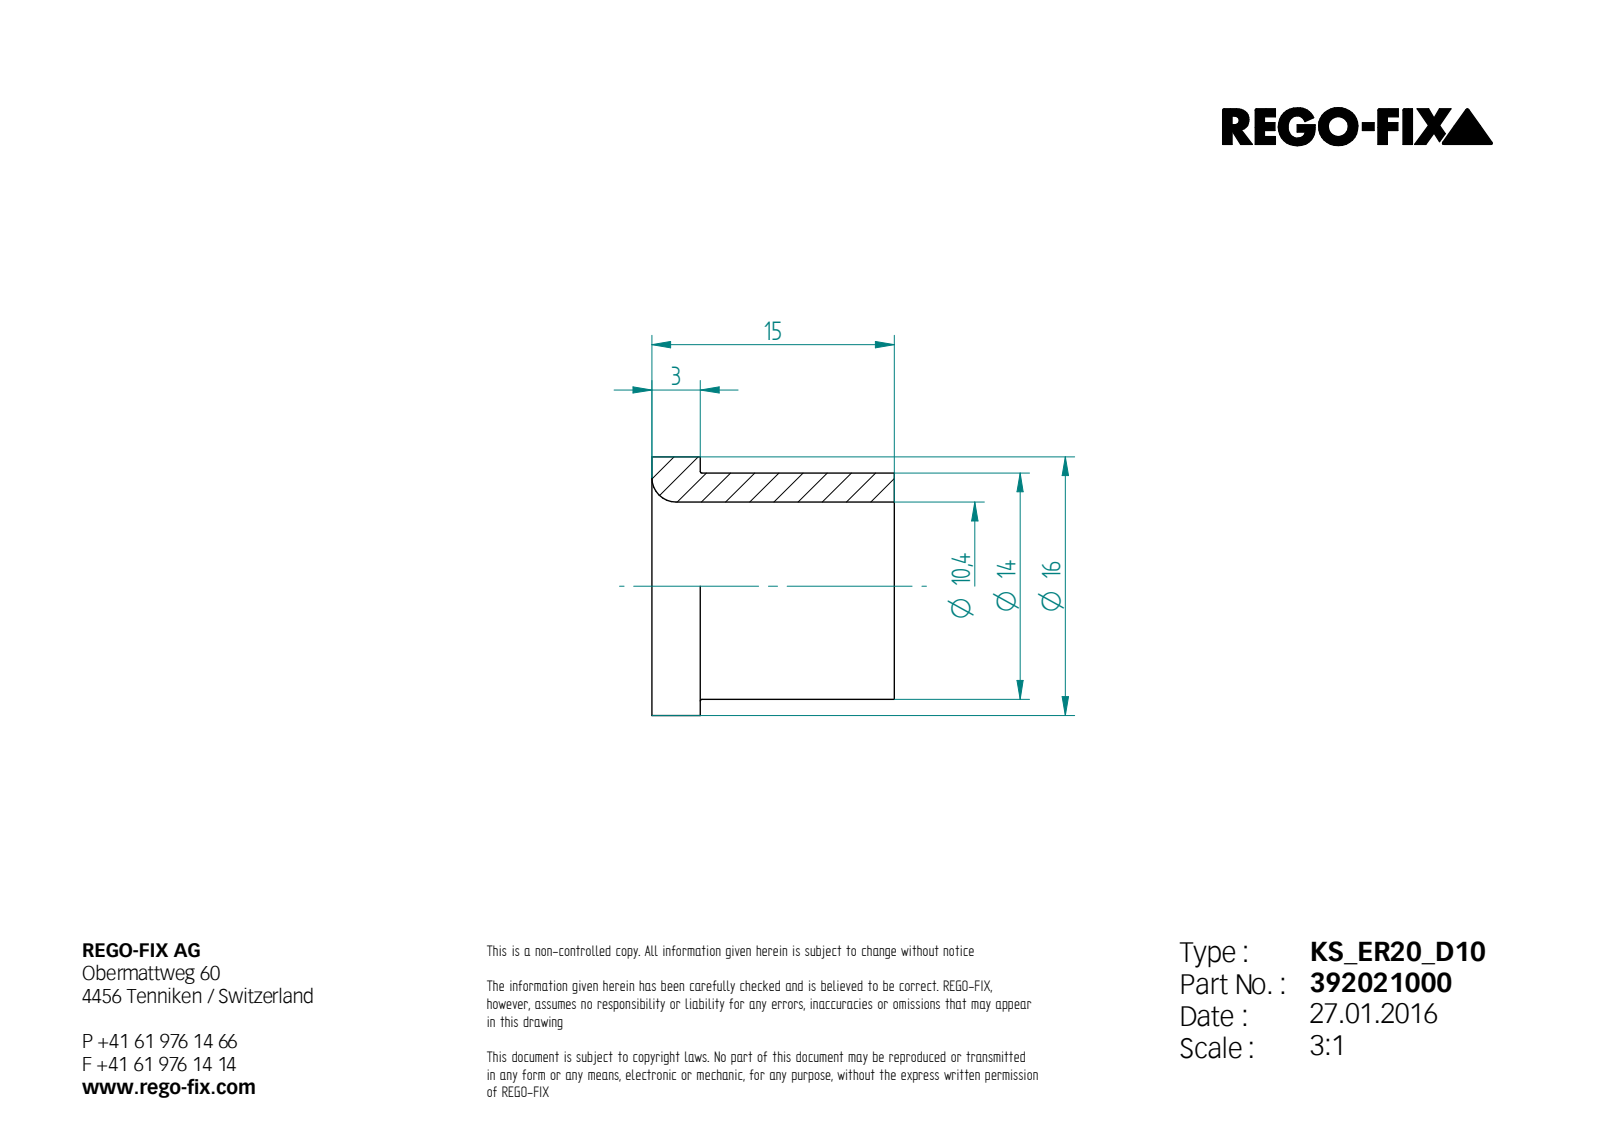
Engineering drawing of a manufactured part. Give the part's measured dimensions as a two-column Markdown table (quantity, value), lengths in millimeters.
| quantity | value |
| --- | --- |
| STEP written by | Unknown (AUTOMOTIVE_DESIGN) |
| units | millimeters |
| bodies | 1 solid, 8 faces (3 planar, 3 cylindrical, 2 other) |
| overall size | 16 × 16 × 15 |
| volume | 1 160 mm³ |
| surface area | 1 379 mm² |
| round holes (diameter × count) | 10.4 × 1 |
| round bosses / shafts (diameter × count) | 16 × 1, 14 × 1 |
| main face-to-face distances | 15, 3, 12 |
